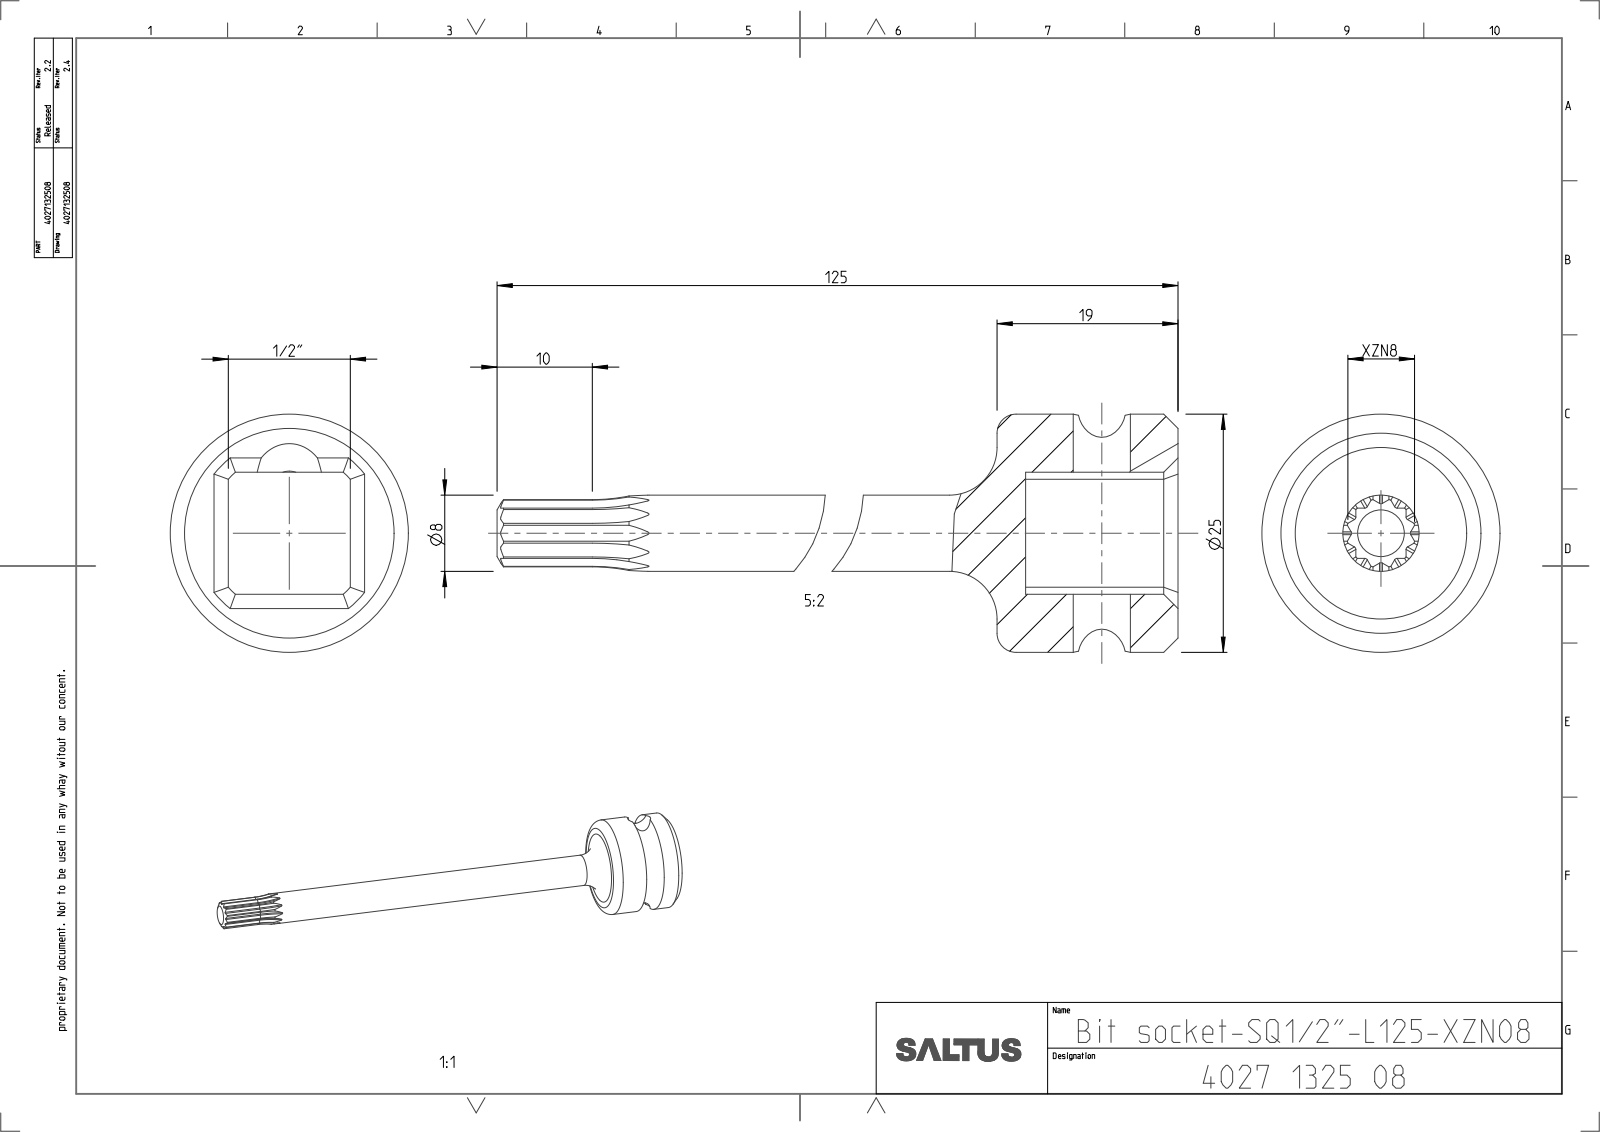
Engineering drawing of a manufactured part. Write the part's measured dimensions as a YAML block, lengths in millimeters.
part_name: "4027132508"
step_written_by: "CREO PARAMETRIC BY PTC INC, 2022414 (CONFIG_CONTROL_DESIGN)"
units: millimeters
bodies: {solids: 1, faces: 138, planar: 37, cylindrical: 39, other: 62}
overall_size: [125, 25, 25]
volume: 10979
surface_area: 5845
round_holes:
  - {diameter: 6, count: 1}
round_bosses_or_shafts:
  - {diameter: 25, count: 1}
  - {diameter: 8, count: 1}
partial_cylinders:
  - {radius: 0.3, count: 12}
  - {radius: 3.62, count: 1}
  - {radius: 4, count: 1}
  - {radius: 8.55, count: 1}
face_to_face_distances: [12.82, 16, 19, 3, 5.28, 3.77, 9.05, 125, 109, 106]
